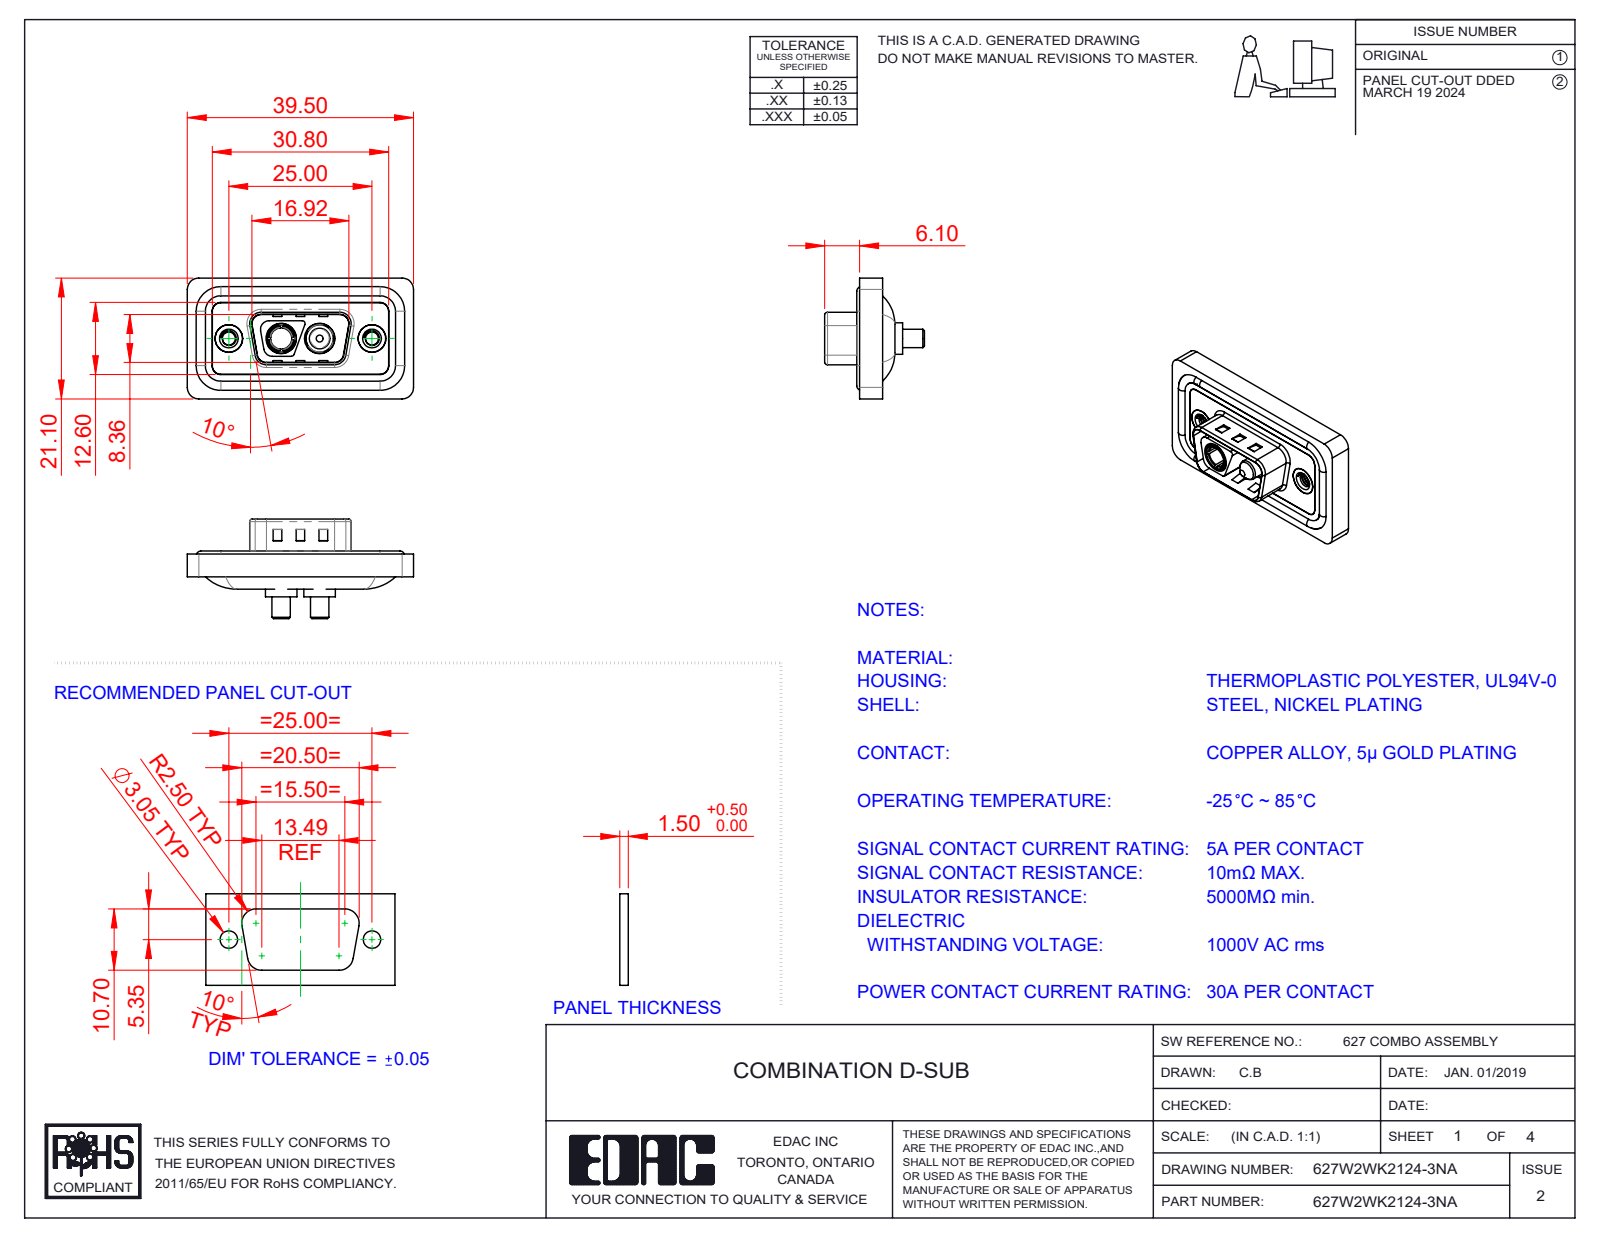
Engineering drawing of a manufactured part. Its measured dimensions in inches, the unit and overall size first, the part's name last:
Units: inches
Overall size (bounding box): 1.555 × 0.831 × 0.685
Round holes (diameter × count): ⌀0.089 ×2, ⌀0.157 ×2, ⌀0.189 ×2, ⌀0.191 ×2, ⌀0.197 ×2, ⌀0.209 ×2, ⌀0.146 ×1
Round bosses / shafts (diameter × count): ⌀0.063 ×4, ⌀0.217 ×2, ⌀0.205 ×2, ⌀0.193 ×2, ⌀0.187 ×2, ⌀0.148 ×2, ⌀0.126 ×2, ⌀0.195 ×1
Partial cylindrical surfaces — rounded edges, fillets, slot ends (radius × count): R0.059 ×24, R0.079 ×18, R0.02 ×10, R0.063 ×8, R0.01 ×4, R0.024 ×4, R0.026 ×4, R0.035 ×4
Main face-to-face distances: 0.016, 0.043, 0.114, 0.02, 0.122, 0.063, 0.059, 0.157, 0.098, 0.071
Hole centre spacings: 0.36, 0.624, 0.265, 0.984
Volume: 0.279 in³ · Surface area: 11.39 in²
Bodies: 11 solids, 532 faces (189 planar, 229 cylindrical, 114 other)
Part name (STEP PRODUCT): 627Combo Shell Front_09 Contacts; 627Combo Housing_2WK2; 627Combo Waterproof Housing_09 Contacts; 627Combo Shell Rear_09 Contacts (+4 more)
STEP written by: SolidWorks 2023 (CONFIG_CONTROL_DESIGN)
